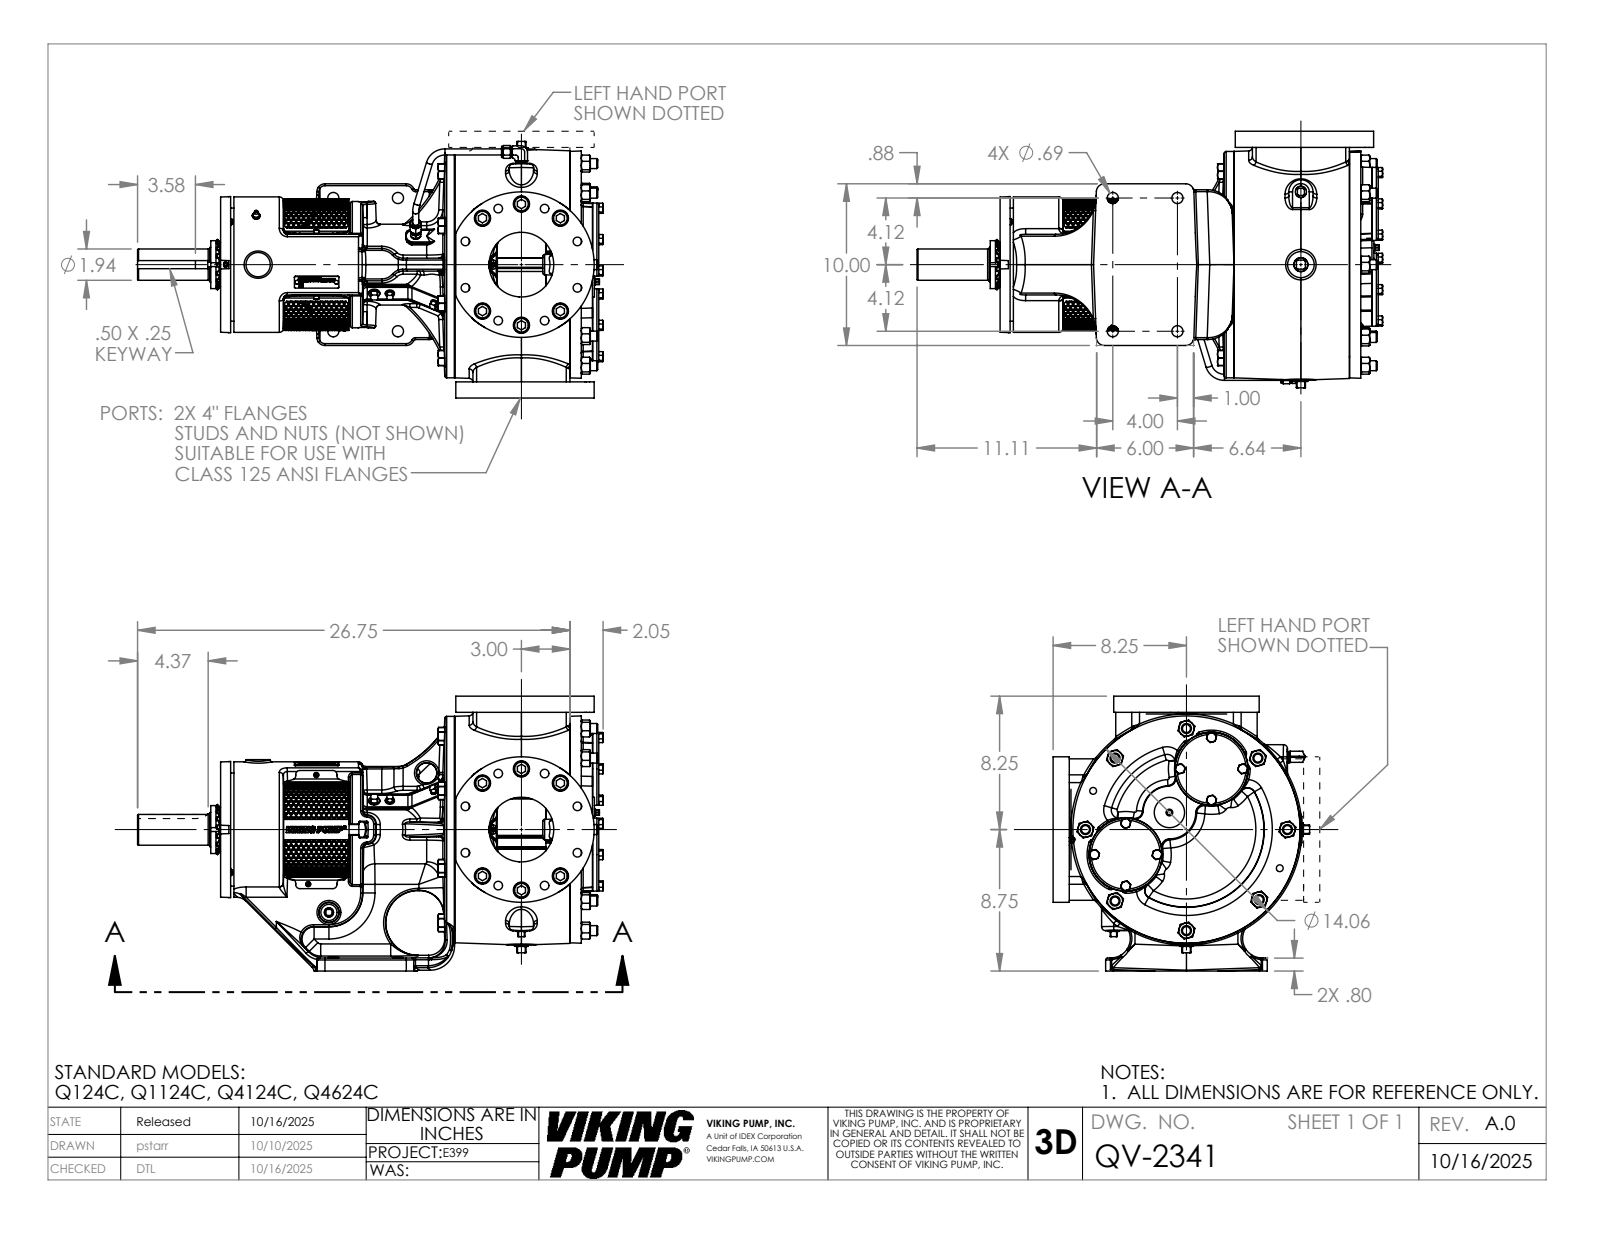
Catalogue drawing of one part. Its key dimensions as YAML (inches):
part_name: "QV-2341"
step_written_by: "SolidWorks 2024 (AUTOMOTIVE_DESIGN)"
units: inches
bodies: {solids: 1, faces: 4173, planar: 1463, cylindrical: 722, other: 1988}
overall_size: [28.804, 17, 15.971]
volume: 2051
surface_area: 2113
round_holes:
  - {diameter: 0.531, count: 16}
  - {diameter: 0.656, count: 12}
  - {diameter: 1, count: 12}
  - {diameter: 0.25, count: 9}
  - {diameter: 0.266, count: 8}
  - {diameter: 1.157, count: 8}
  - {diameter: 0.688, count: 4}
  - {diameter: 0.159, count: 2}
  - {diameter: 0.313, count: 2}
  - {diameter: 0.422, count: 2}
  - {diameter: 4, count: 2}
  - {diameter: 0.453, count: 1}
round_bosses_or_shafts:
  - {diameter: 0.937, count: 12}
  - {diameter: 0.625, count: 9}
  - {diameter: 0.617, count: 8}
  - {diameter: 0.625, count: 3}
  - {diameter: 0.375, count: 3}
  - {diameter: 0.312, count: 3}
  - {diameter: 0.19, count: 3}
  - {diameter: 9, count: 2}
partial_cylinders:
  - {radius: 0.12, count: 60}
  - {radius: 0.25, count: 22}
  - {radius: 0.015, count: 18}
  - {radius: 0.092, count: 18}
  - {radius: 0.07, count: 16}
  - {radius: 0.75, count: 16}
  - {radius: 0.5, count: 13}
  - {radius: 0.24, count: 10}
face_to_face_distances: [17, 22.317, 3.82, 18.498, 1, 23.398, 19.578, 1.081, 7.972, 4.153]
hole_center_spacings: [3.75, 5.303, 2.87, 6.929, 2.079, 5.783, 7.5, 1.463]
